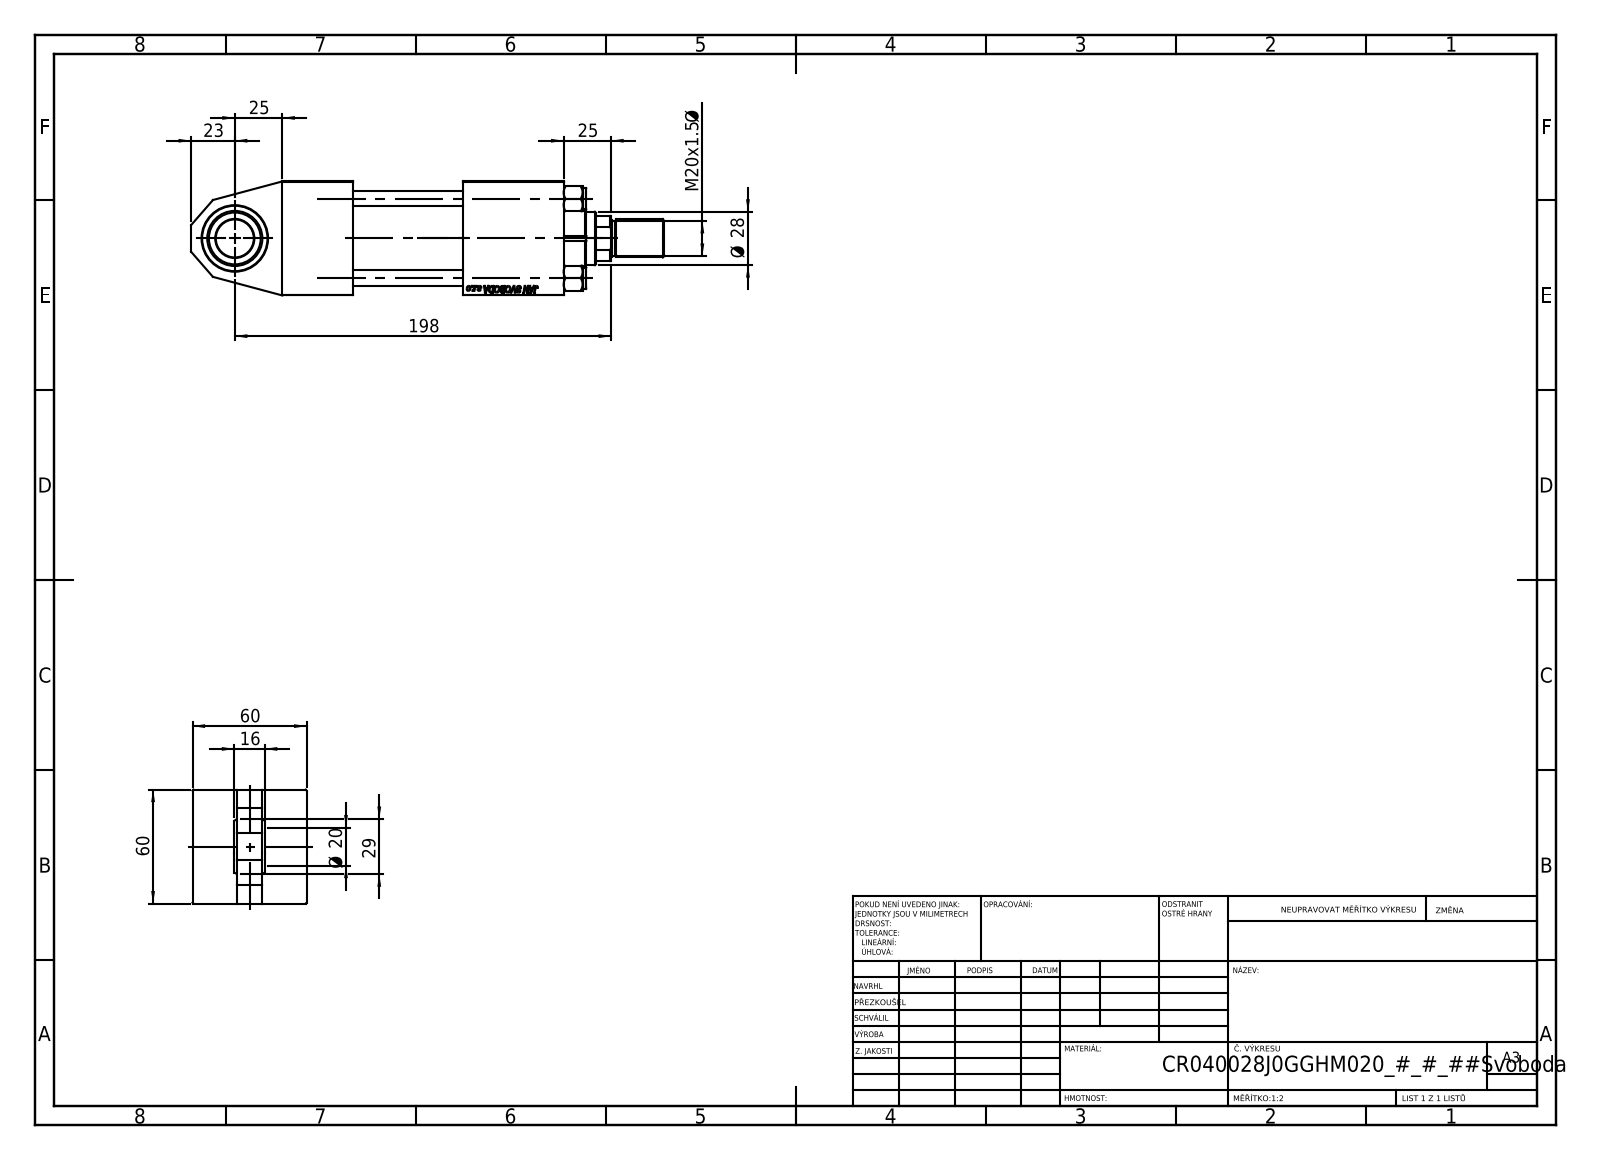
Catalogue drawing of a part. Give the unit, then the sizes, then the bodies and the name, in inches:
Units: inches
Overall size (bounding box): 9.803 × 2.362 × 2.362
Round holes (diameter × count): ⌀0.315 ×4, ⌀0.098 ×2, ⌀0.276 ×2, ⌀0.656 ×2, ⌀0.945 ×2, ⌀0.728 ×1, ⌀0.787 ×1, ⌀1.102 ×1, ⌀1.22 ×1, ⌀1.378 ×1, ⌀1.575 ×1, ⌀1.772 ×1
Round bosses / shafts (diameter × count): ⌀0.433 ×4, ⌀1.811 ×1, ⌀1.654 ×1, ⌀0.787 ×1, ⌀0.709 ×1
Partial cylindrical surfaces — rounded edges, fillets, slot ends (radius × count): R0.531 ×1
Main face-to-face distances: 2.362, 1.437, 0.925, 1.457, 2.087, 2.283, 3.74, 0.512, 5.827, 4.37
Hole centre spacings: 0.821, 1.161, 1.642, 1.832, 0.817, 2.322, 1.634, 3.642
Volume: 28.06 in³ · Surface area: 190.9 in²
Bodies: 13 solids, 1161 faces (523 planar, 92 cylindrical, 546 other)
Part name (STEP PRODUCT): NUT_M5_J; V215CR_J_Body; V215_VC_A; V215CR_VCP_J (+3 more)
STEP written by: SolidWorks 2019 (CONFIG_CONTROL_DESIGN)
